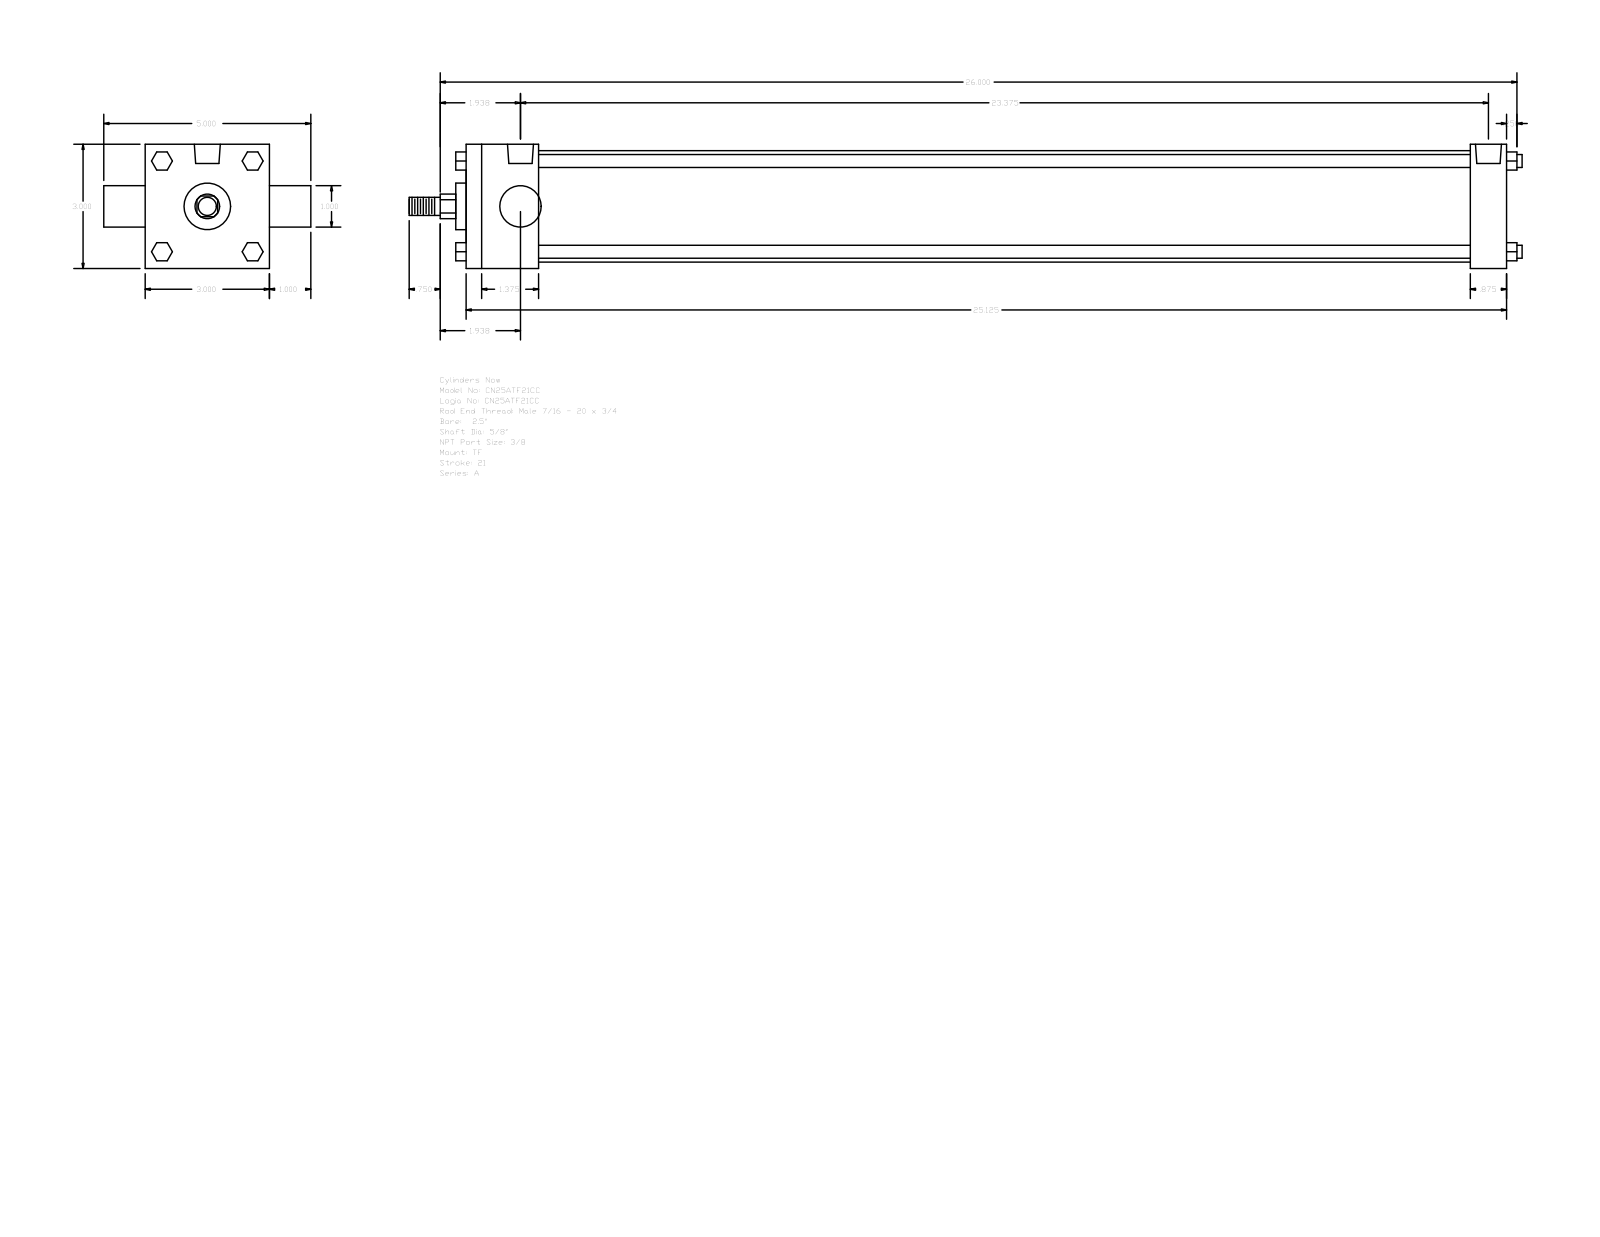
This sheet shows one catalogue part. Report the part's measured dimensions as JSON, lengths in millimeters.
{"part_name": "A_TF__0250_0.625", "step_written_by": "GSSL Pune (CONFIG_CONTROL_DESIGN)", "units": "millimeters", "bodies": {"solids": 0, "faces": 120, "planar": 92, "cylindrical": 28, "other": 0}, "overall_size": [682.62, 127, 76.2], "round_holes": [[5.56, 3], [15.93, 2]], "round_bosses_or_shafts": [[7.94, 4], [68.33, 1], [28.57, 1], [25.4, 1], [15.88, 1], [11.11, 1]], "partial_cylinders_radius": [[7.54, 1]], "face_to_face_distances": [76.2, 638.17, 44.45, 615.95, 571.5, 593.72, 22.22, 25.4, 101.6, 6.35], "hole_center_spacings": [2.38, 596.11, 593.73, 598.49]}
